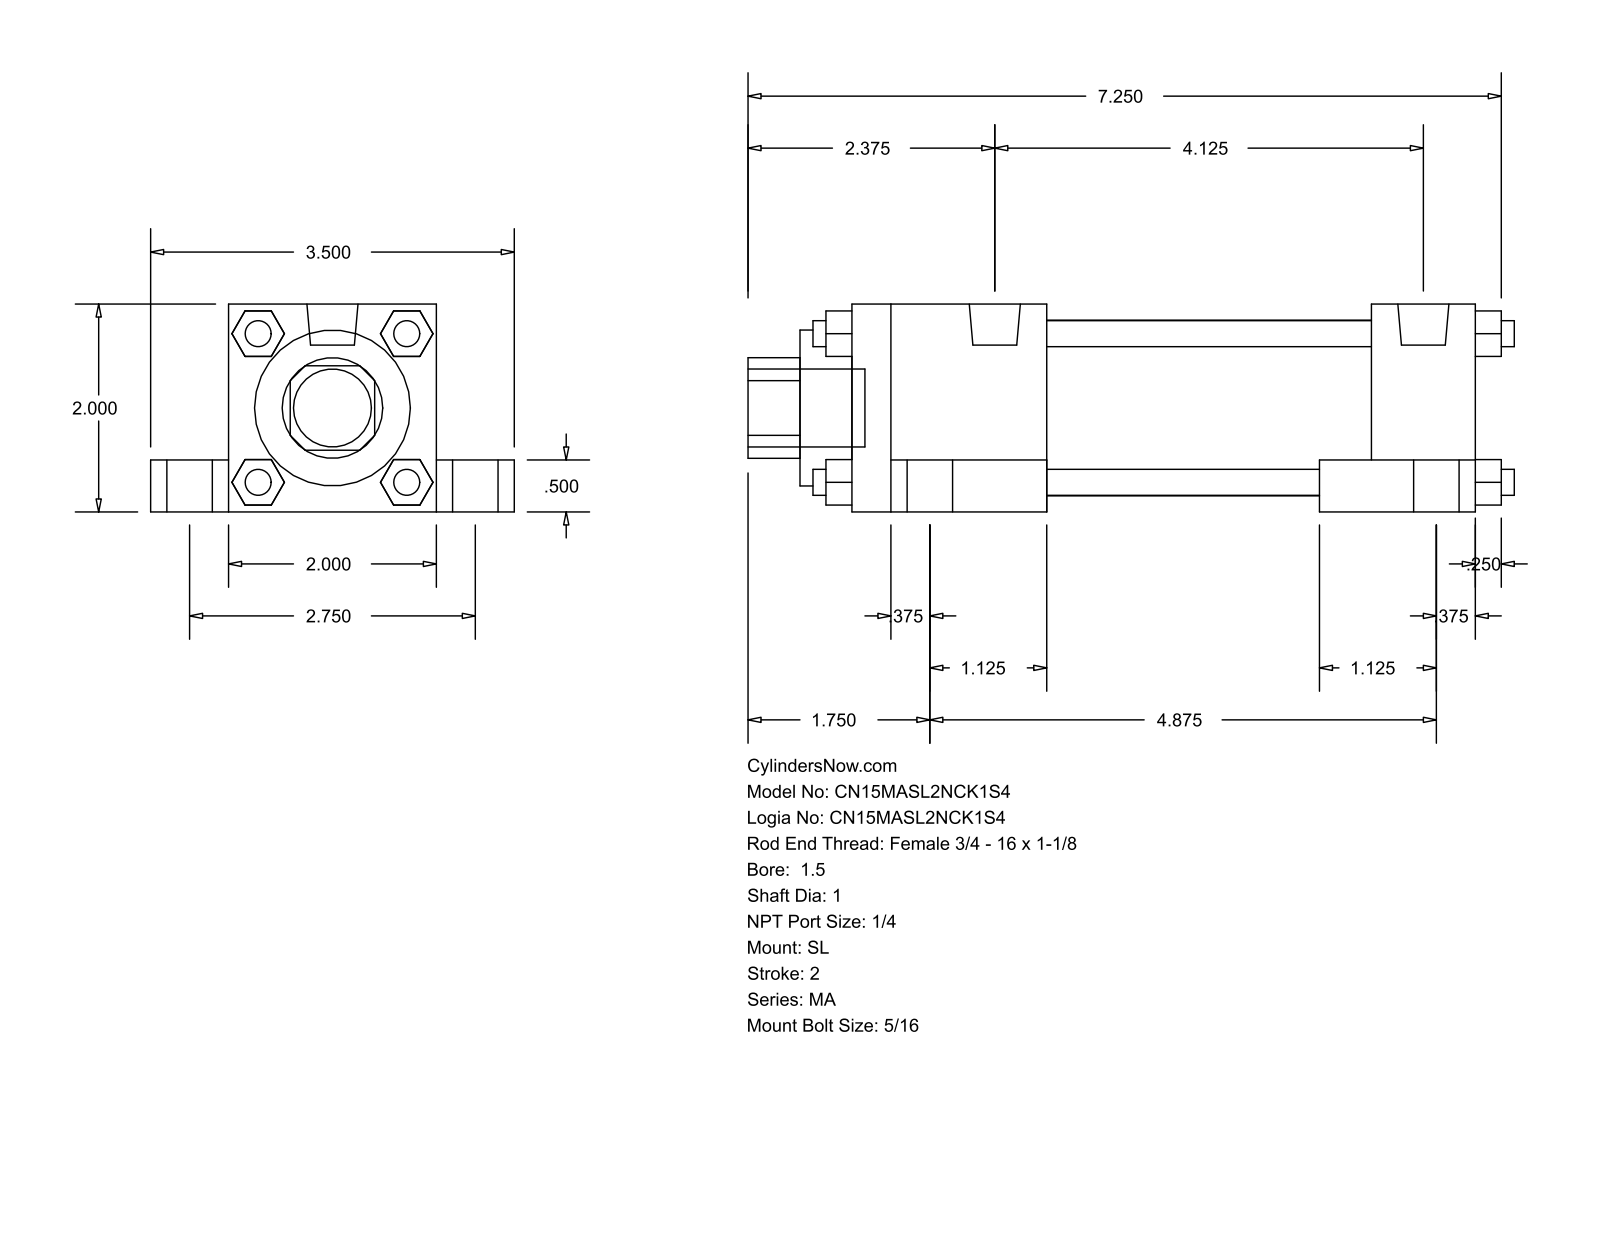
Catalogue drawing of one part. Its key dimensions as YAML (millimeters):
part_name: "MA_SL__0150_1"
step_written_by: "GSSL Pune (CONFIG_CONTROL_DESIGN)"
units: millimeters
bodies: {solids: 0, faces: 148, planar: 112, cylindrical: 36, other: 0}
overall_size: [187.32, 88.9, 50.8]
round_holes:
  - {diameter: 25.4, count: 1}
  - {diameter: 38.1, count: 1}
  - {diameter: 42.93, count: 1}
round_bosses_or_shafts:
  - {diameter: 17.46, count: 4}
  - {diameter: 11.11, count: 4}
  - {diameter: 7.94, count: 4}
  - {diameter: 6.35, count: 4}
  - {diameter: 12.49, count: 2}
  - {diameter: 19.05, count: 1}
partial_cylinders:
  - {radius: 12.29, count: 1}
face_to_face_distances: [50.8, 12.7, 19.05, 9.52, 69.85, 38.1, 6.35, 152.4, 25.4, 127]
